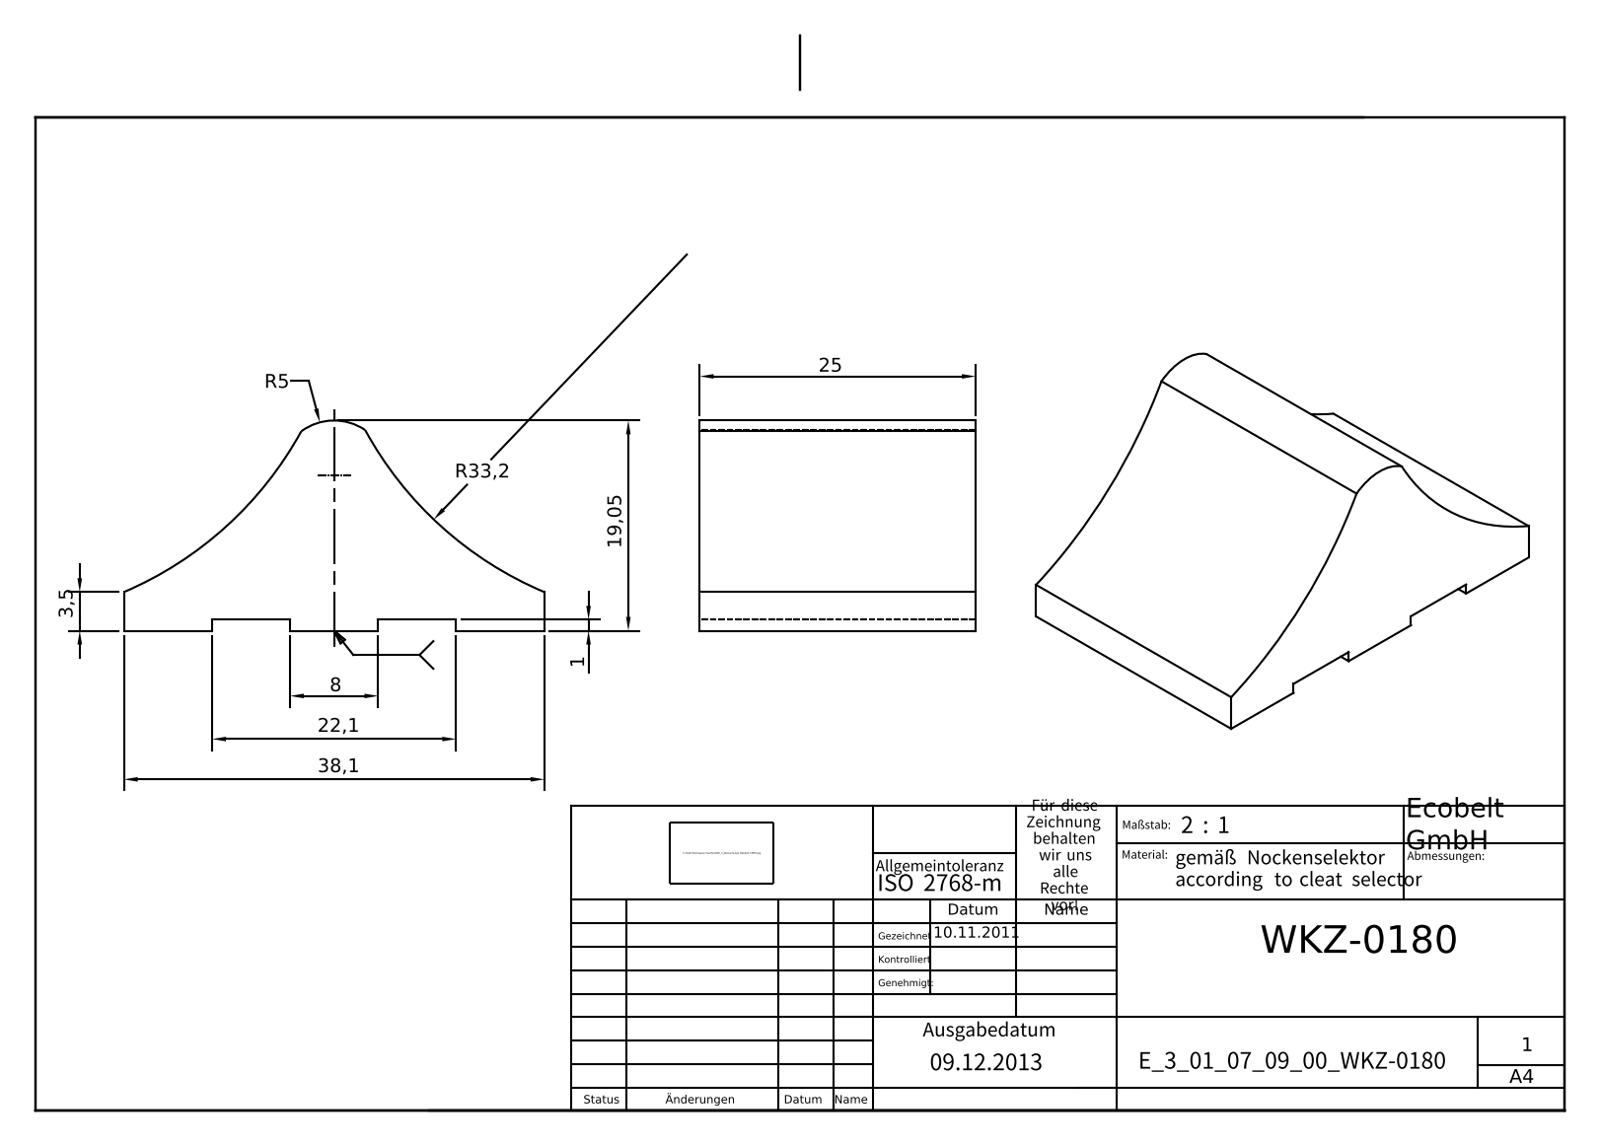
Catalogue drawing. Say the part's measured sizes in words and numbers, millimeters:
The part is named "E_3_01_07_09_00_WKZ-0180". Its 3-D file was written by "Autodesk Inventor 2025 (AUTOMOTIVE_DESIGN)". It is 1 solid with 16 faces: 13 planar, 3 cylindrical and 0 other. Overall it measures 38.1 by 25 by 19.05 millimeters. Its volume is 9 753 cubic millimeters and its surface area 3 272 square millimeters. Partial cylindrical surfaces (rounded edges, fillets, slot ends): 2 of radius 33.2, 1 of radius 5. The main face-to-face distances are 25, 1, 15.05, 38.1, 8, 30.1, 23.05, 7.05, 22.1.
